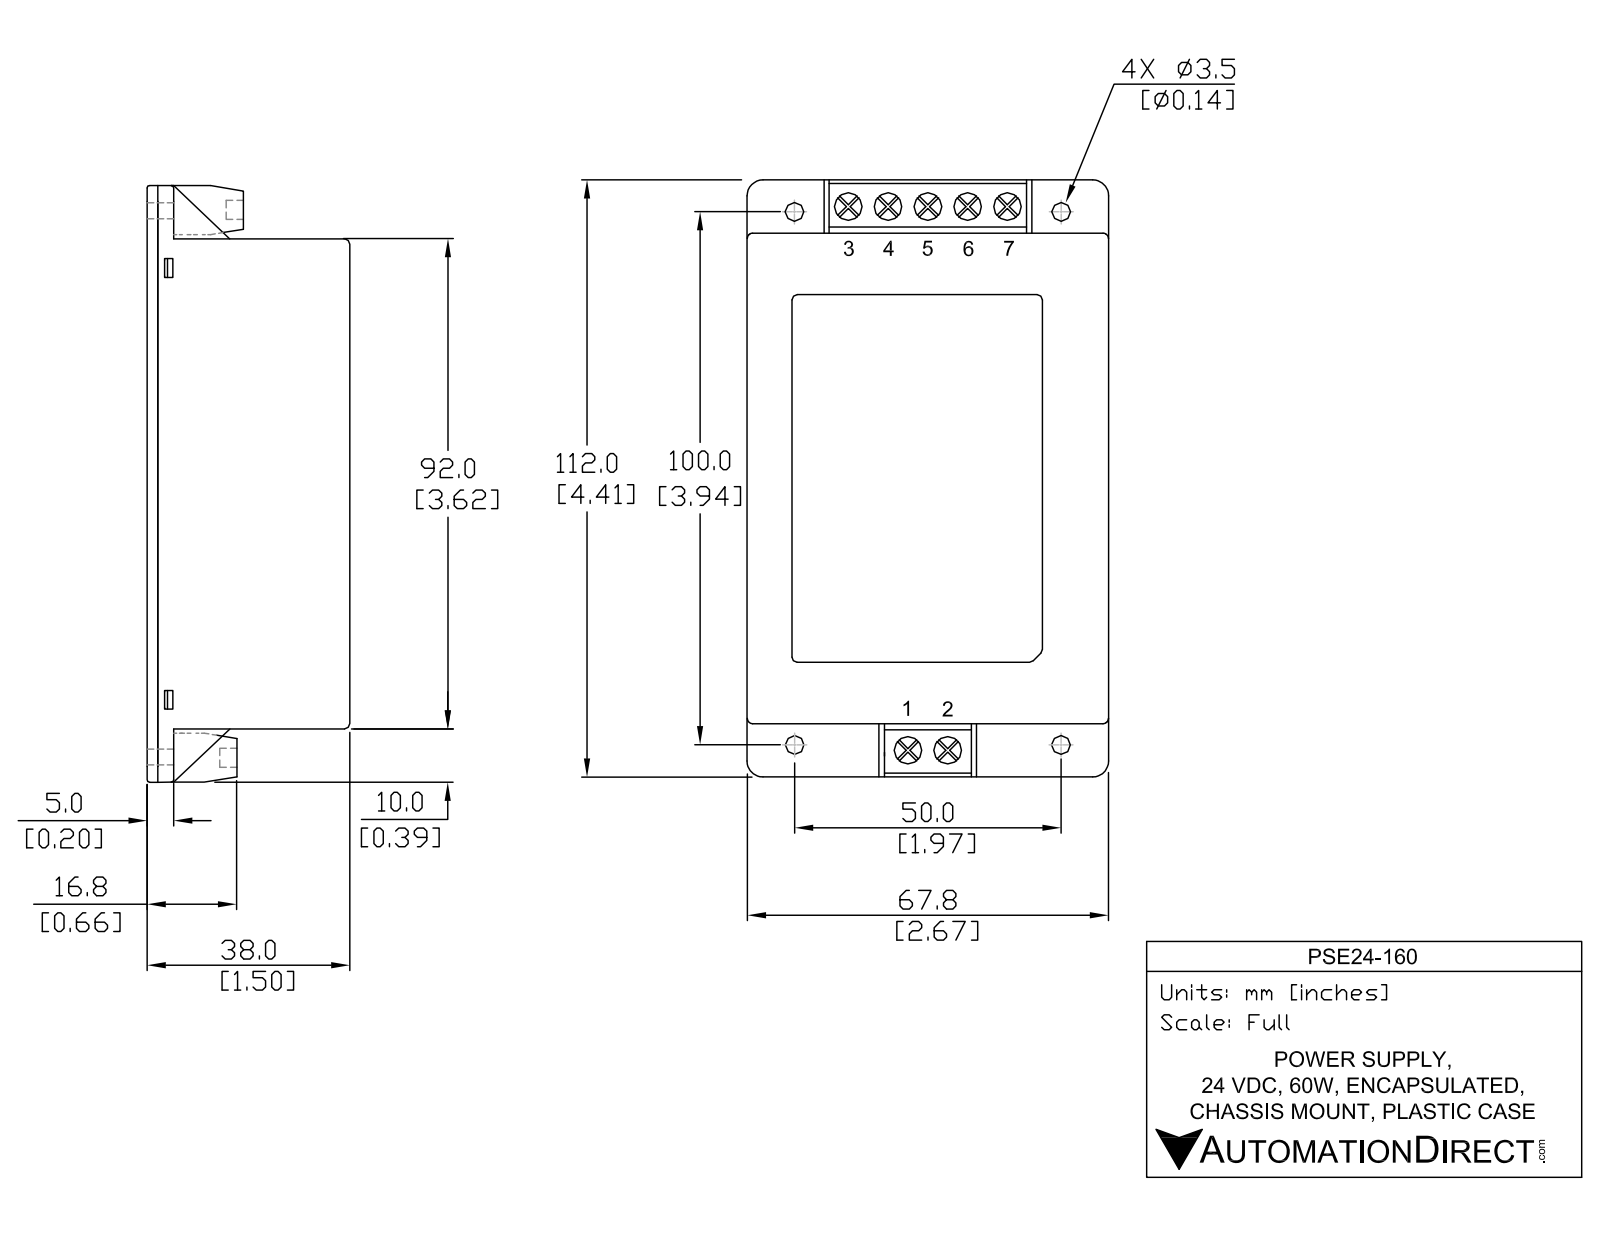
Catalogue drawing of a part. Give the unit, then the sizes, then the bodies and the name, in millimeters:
Units: millimetres
Overall size (bounding box): 112 × 67.8 × 38.1
Round holes (diameter × count): ⌀5.1 ×7, ⌀3.6 ×4
Partial cylindrical surfaces — rounded edges, fillets, slot ends (radius × count): R0.8 ×20, R3.2 ×4
Main face-to-face distances: 2, 2, 36.1, 67.8, 38, 36, 38.1, 36.1, 91.9, 0.4
Hole centre spacings: 6.6, 13.2, 6.6, 21.7, 28.3, 50, 100.1, 102
Volume: 248 800 mm³ · Surface area: 45 010 mm²
Bodies: 2 solids, 374 faces (246 planar, 62 cylindrical, 66 other)
Part name (STEP PRODUCT): PSE24-160
STEP written by: SolidWorks 2011 (CONFIG_CONTROL_DESIGN)
